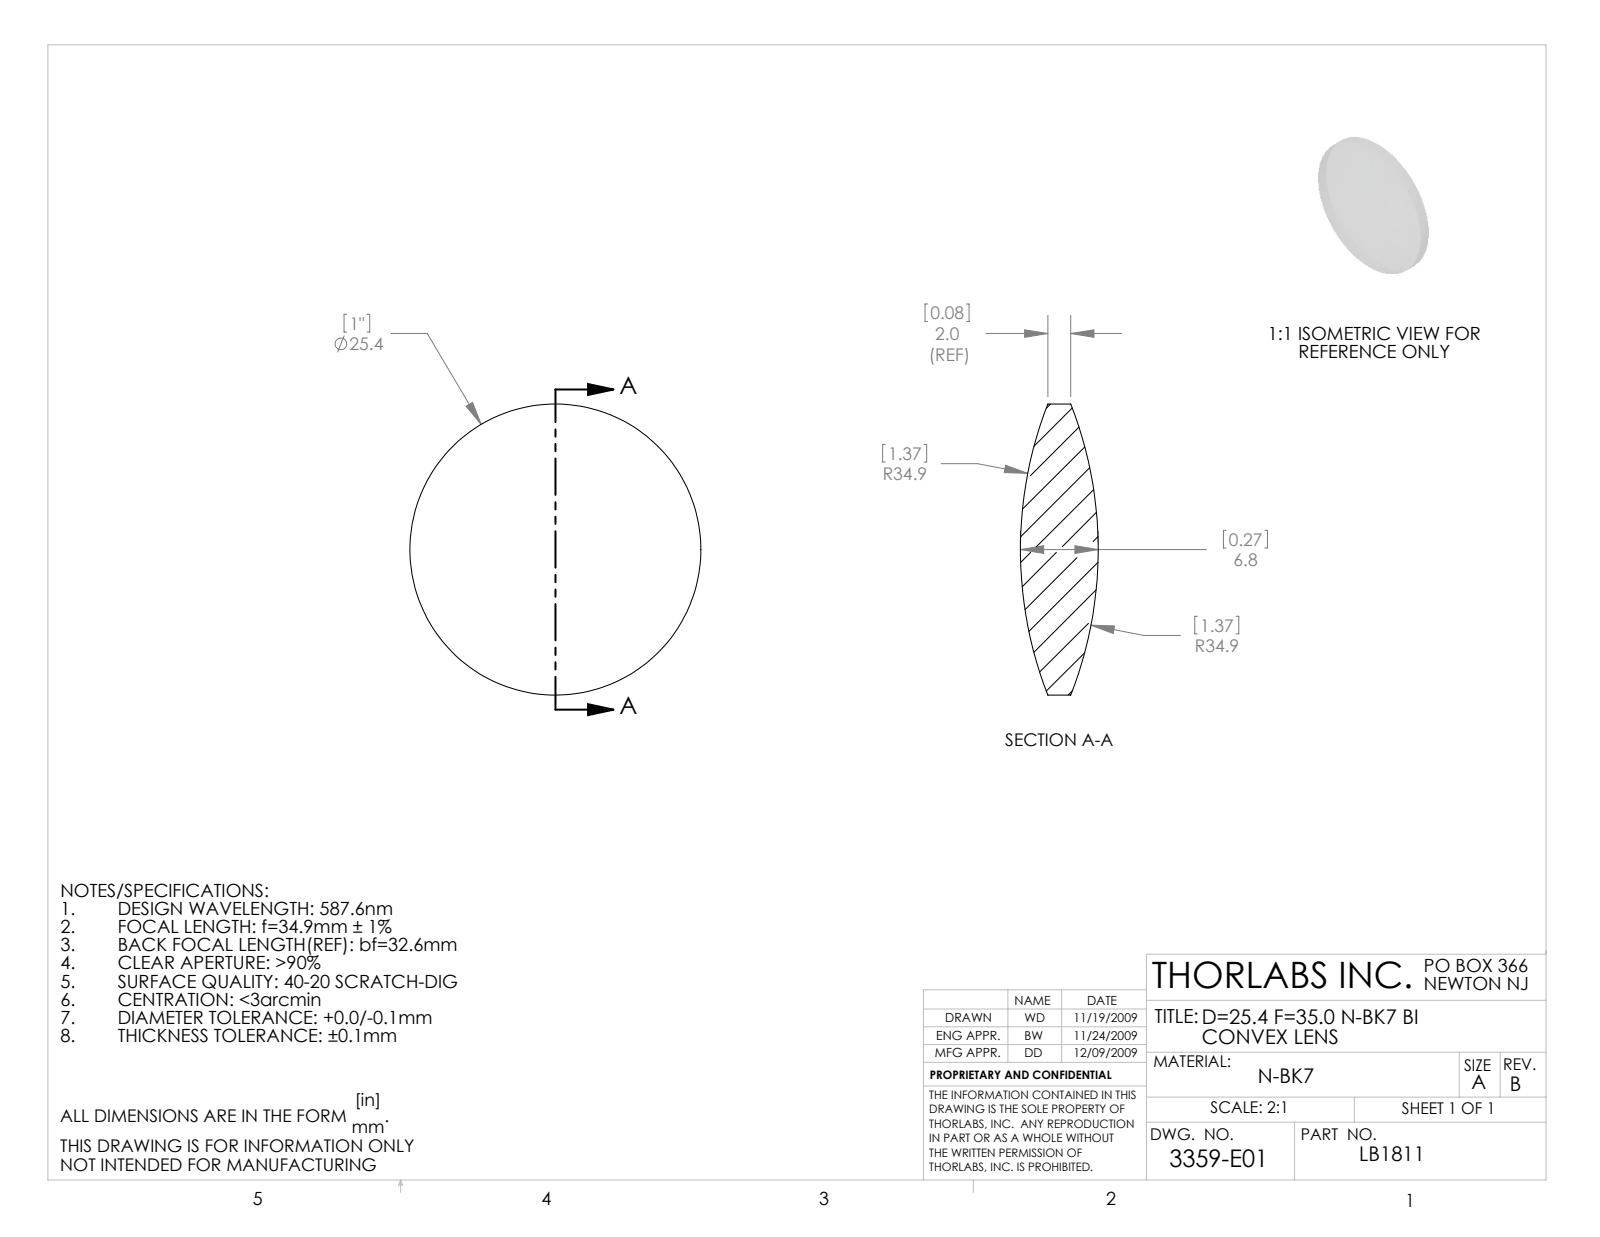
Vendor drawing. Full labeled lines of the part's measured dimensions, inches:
Part name (STEP PRODUCT): 3359-E0W
STEP written by: SolidWorks 2009 (AUTOMOTIVE_DESIGN)
Units: inches
Bodies: 1 solid, 6 faces (0 planar, 2 cylindrical, 4 other)
Overall size (bounding box): 1 × 1 × 0.267
Volume: 0.137 in³ · Surface area: 1.874 in²
Round bosses / shafts (diameter × count): ⌀1 ×1
